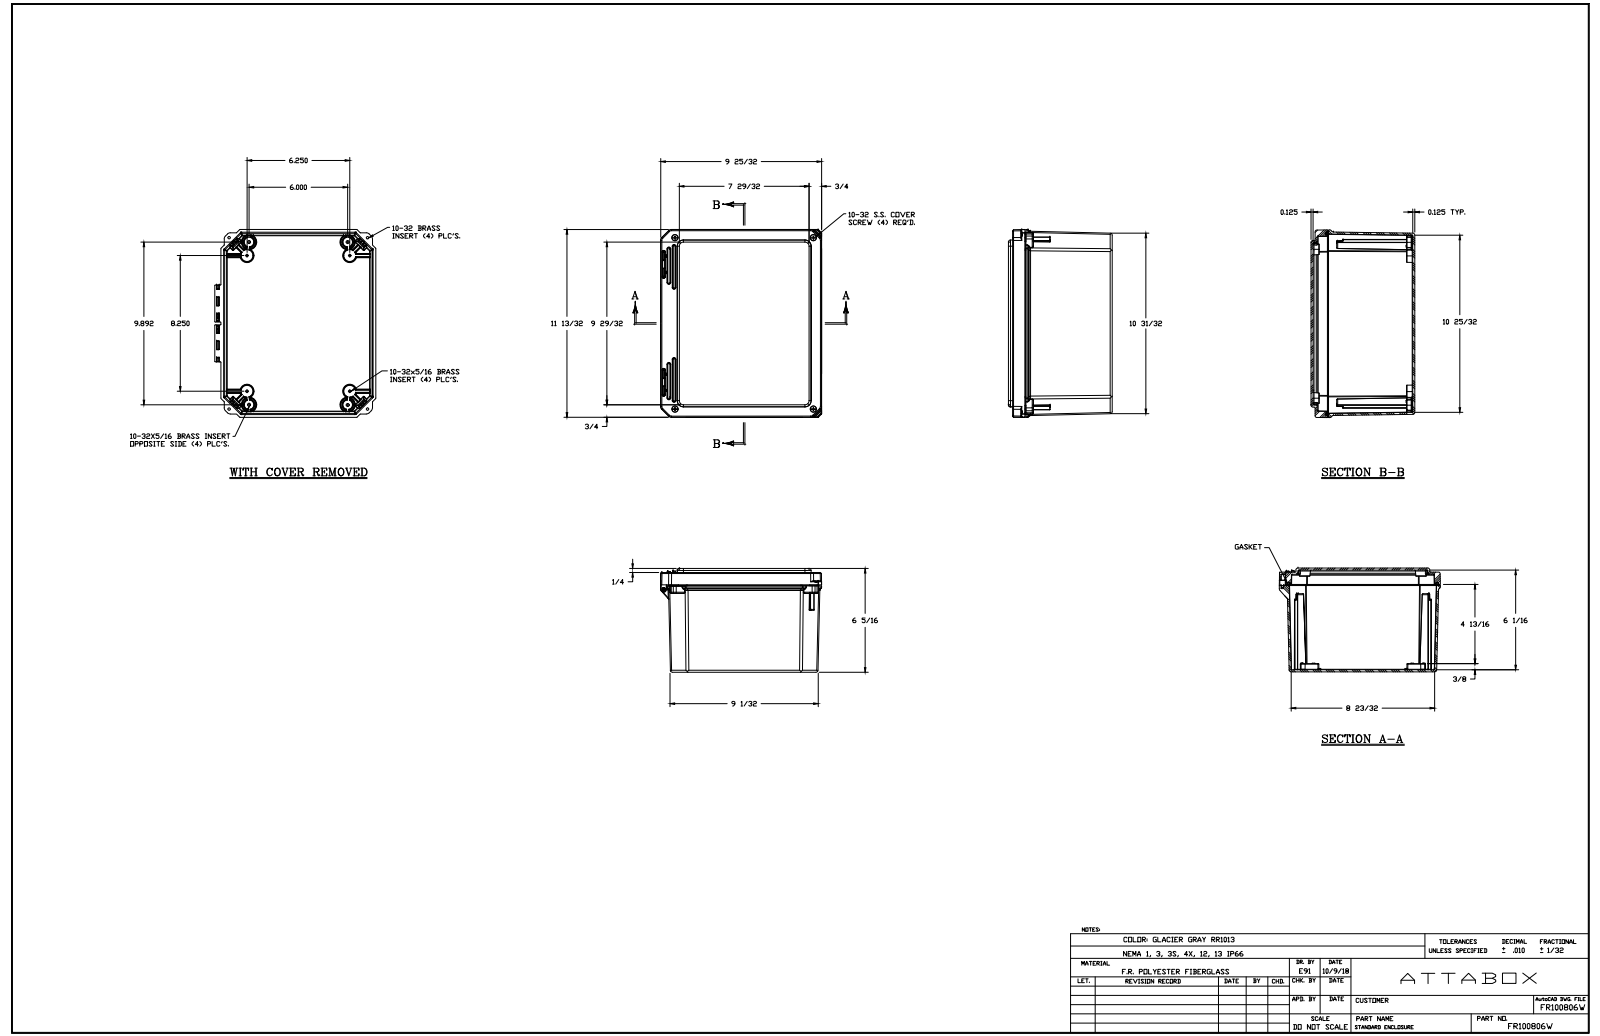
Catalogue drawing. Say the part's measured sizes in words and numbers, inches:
The part is named "FR100806W". Its 3-D file was written by "SolidWorks 2018 (AUTOMOTIVE_DESIGN)". It is 23 solids with 2041 faces: 665 planar, 750 cylindrical and 626 other. Overall it measures 11.429 by 9.8 by 6.31 inches. Its volume is 69.88 cubic inches and its surface area 979.6 square inches. Round holes: 12 of diameter 0.156, 8 of diameter 0.152, 4 of diameter 0.252, 4 of diameter 0.253, 2 of diameter 0.219, 2 of diameter 0.227, 2 of diameter 0.313, 1 of diameter 0.137. Round bosses or shafts: 12 of diameter 0.246, 4 of diameter 0.87, 4 of diameter 0.45, 4 of diameter 0.199, 1 of diameter 0.435, 1 of diameter 0.435. Partial cylindrical surfaces (rounded edges, fillets, slot ends): 157 of radius 0.01, 80 of radius 0.005, 57 of radius 0.02, 44 of radius 0.03, 24 of radius 0.03, 24 of radius 0.09, 23 of radius 0.096, 22 of radius 0.125. The main face-to-face distances are 0.125, 6.185, 0.127, 0.126, 6.31, 6.061, 0.25, 5.935, 0.125, 6.06. The hole center spacings are 0.831, 6.18, 7.416, 9.072, 9.399, 11.873, 7.216, 10.35.
